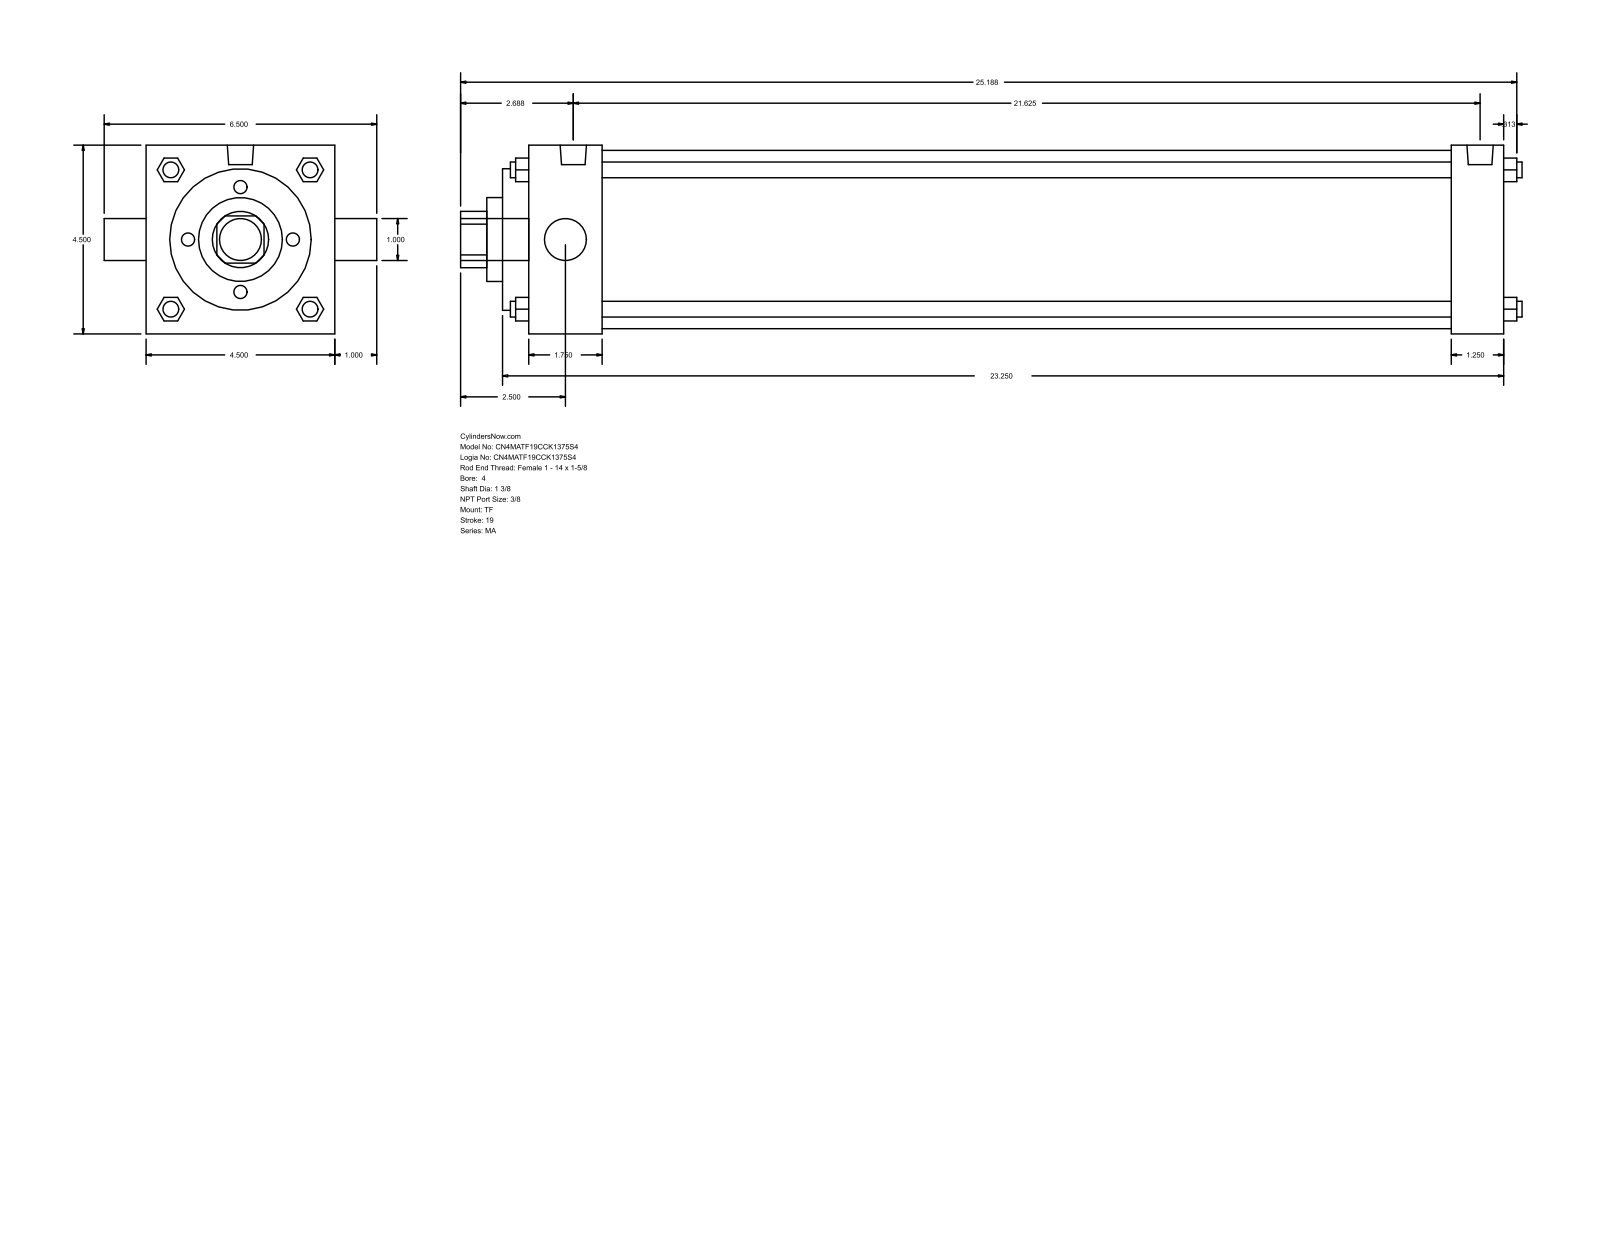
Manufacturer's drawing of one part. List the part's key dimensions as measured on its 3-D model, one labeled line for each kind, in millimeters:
Part name (STEP PRODUCT): MA_TF__0400_1.375
STEP written by: GSSL Pune (CONFIG_CONTROL_DESIGN)
Units: millimetres
Bodies: 0 solids, 122 faces (93 planar, 29 cylindrical, 0 other)
Overall size (bounding box): 642.94 × 165.1 × 114.3
Round holes (diameter × count): ⌀25.4 ×1, ⌀34.92 ×1, ⌀50.8 ×1, ⌀85.72 ×1, ⌀107.95 ×1
Round bosses / shafts (diameter × count): ⌀9.53 ×4, ⌀11.11 ×3, ⌀15.93 ×2, ⌀25.4 ×1
Partial cylindrical surfaces — rounded edges, fillets, slot ends (radius × count): R17.06 ×1
Main face-to-face distances: 114.3, 590.56, 15.87, 606.43, 574.68, 558.81, 31.75, 60.32, 44.45, 514.36
